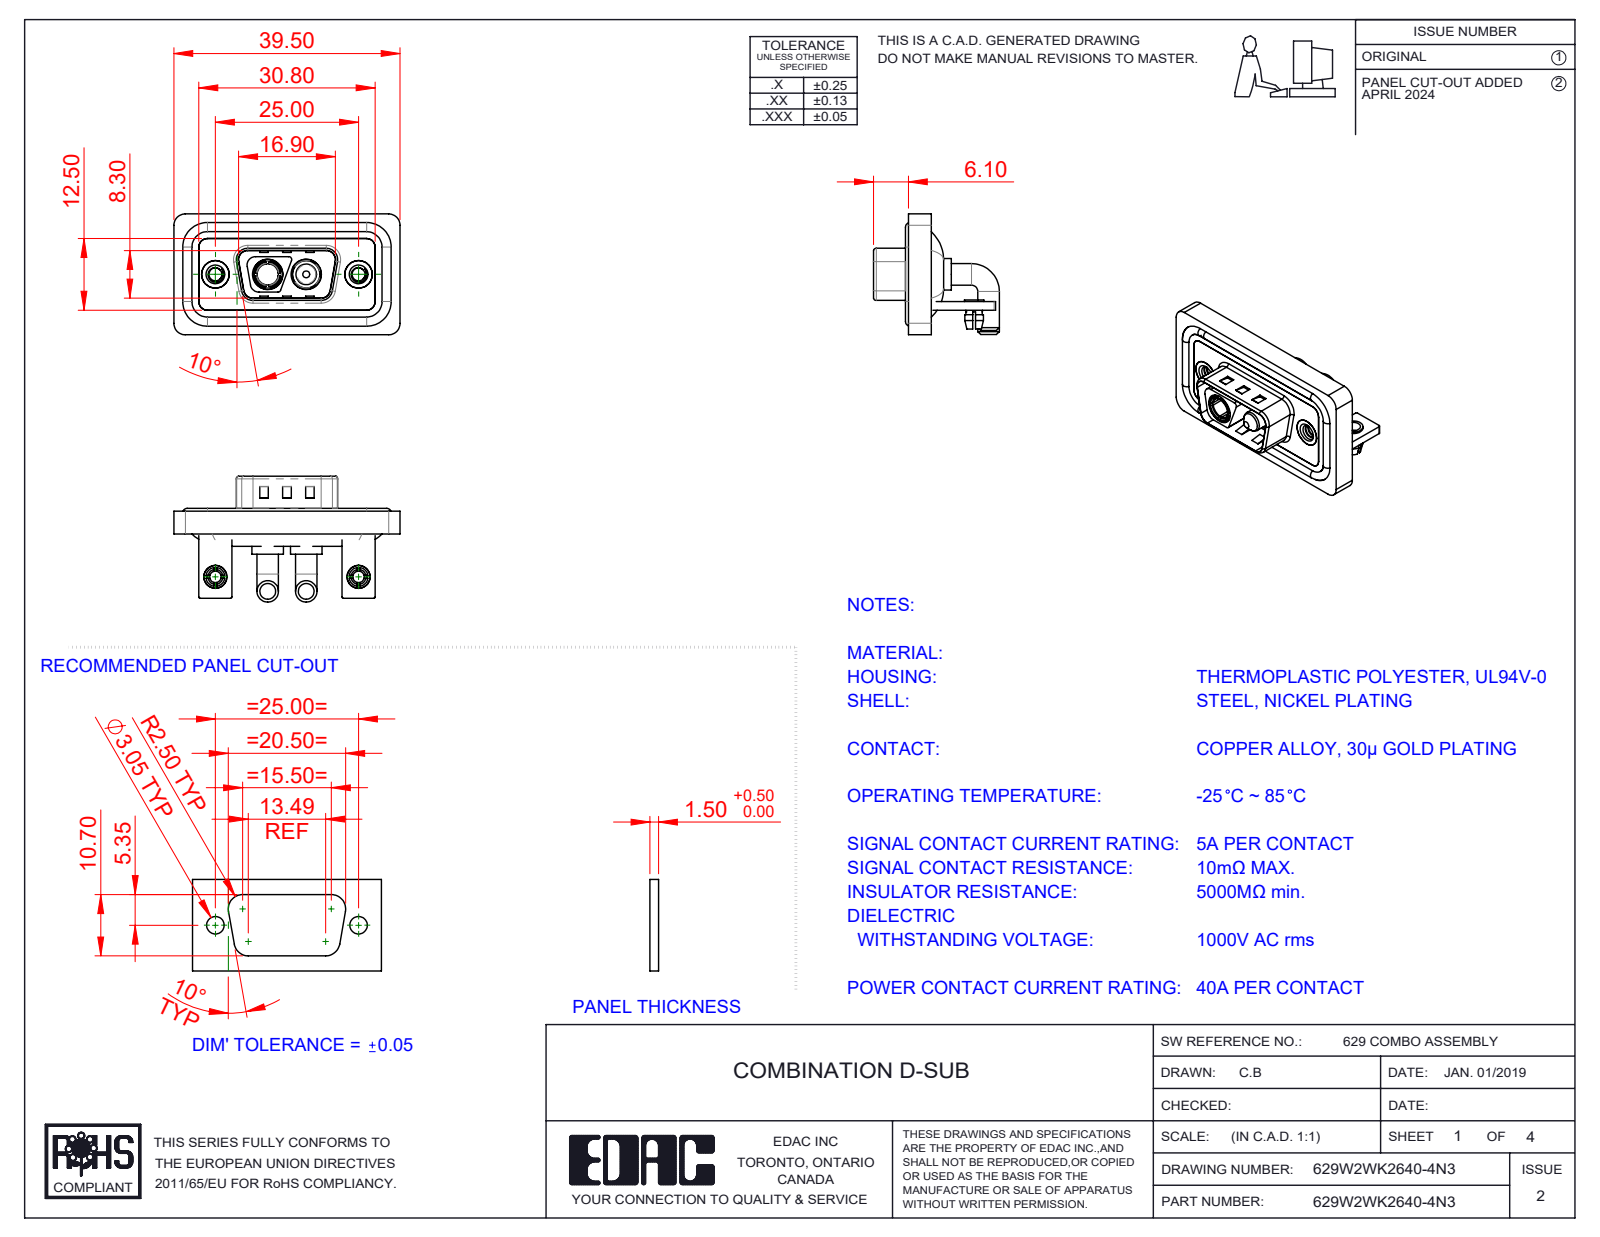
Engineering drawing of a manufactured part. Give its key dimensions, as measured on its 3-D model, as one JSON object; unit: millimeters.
{"part_name": "629Combo Housing_2WK2; 629Combo Threaded Rivet_3; 629W2WK2640-4N3; Power Socket_40A RA (+6 more)", "step_written_by": "SolidWorks 2023 (CONFIG_CONTROL_DESIGN)", "units": "millimeters", "bodies": {"solids": 15, "faces": 674, "planar": 257, "cylindrical": 281, "other": 136}, "overall_size": [39.5, 21.98, 21.1], "volume_mm3": 5145, "surface_area_mm2": 8419, "round_holes": [[2, 2], [2.26, 2], [2.5, 2], [3.2, 2], [4, 2], [4.8, 2], [4.85, 2], [5, 2], [5.3, 2], [3.7, 1]], "round_bosses_or_shafts": [[3.75, 4], [1.6, 4], [5.5, 2], [5.2, 2], [4.9, 2], [4.75, 2], [4, 2], [3.4, 2]], "partial_cylinders_radius": [[1.5, 20], [2, 19], [0.25, 16], [0.5, 11], [1.6, 8], [0.6, 4], [0.65, 4], [0.9, 4]], "face_to_face_distances": [0.4, 1.5, 2.9, 0.8, 1.1, 1.2, 2.1, 1.6, 3.7, 2.5], "hole_center_spacings": [9.14, 15.86, 25, 6.72]}
